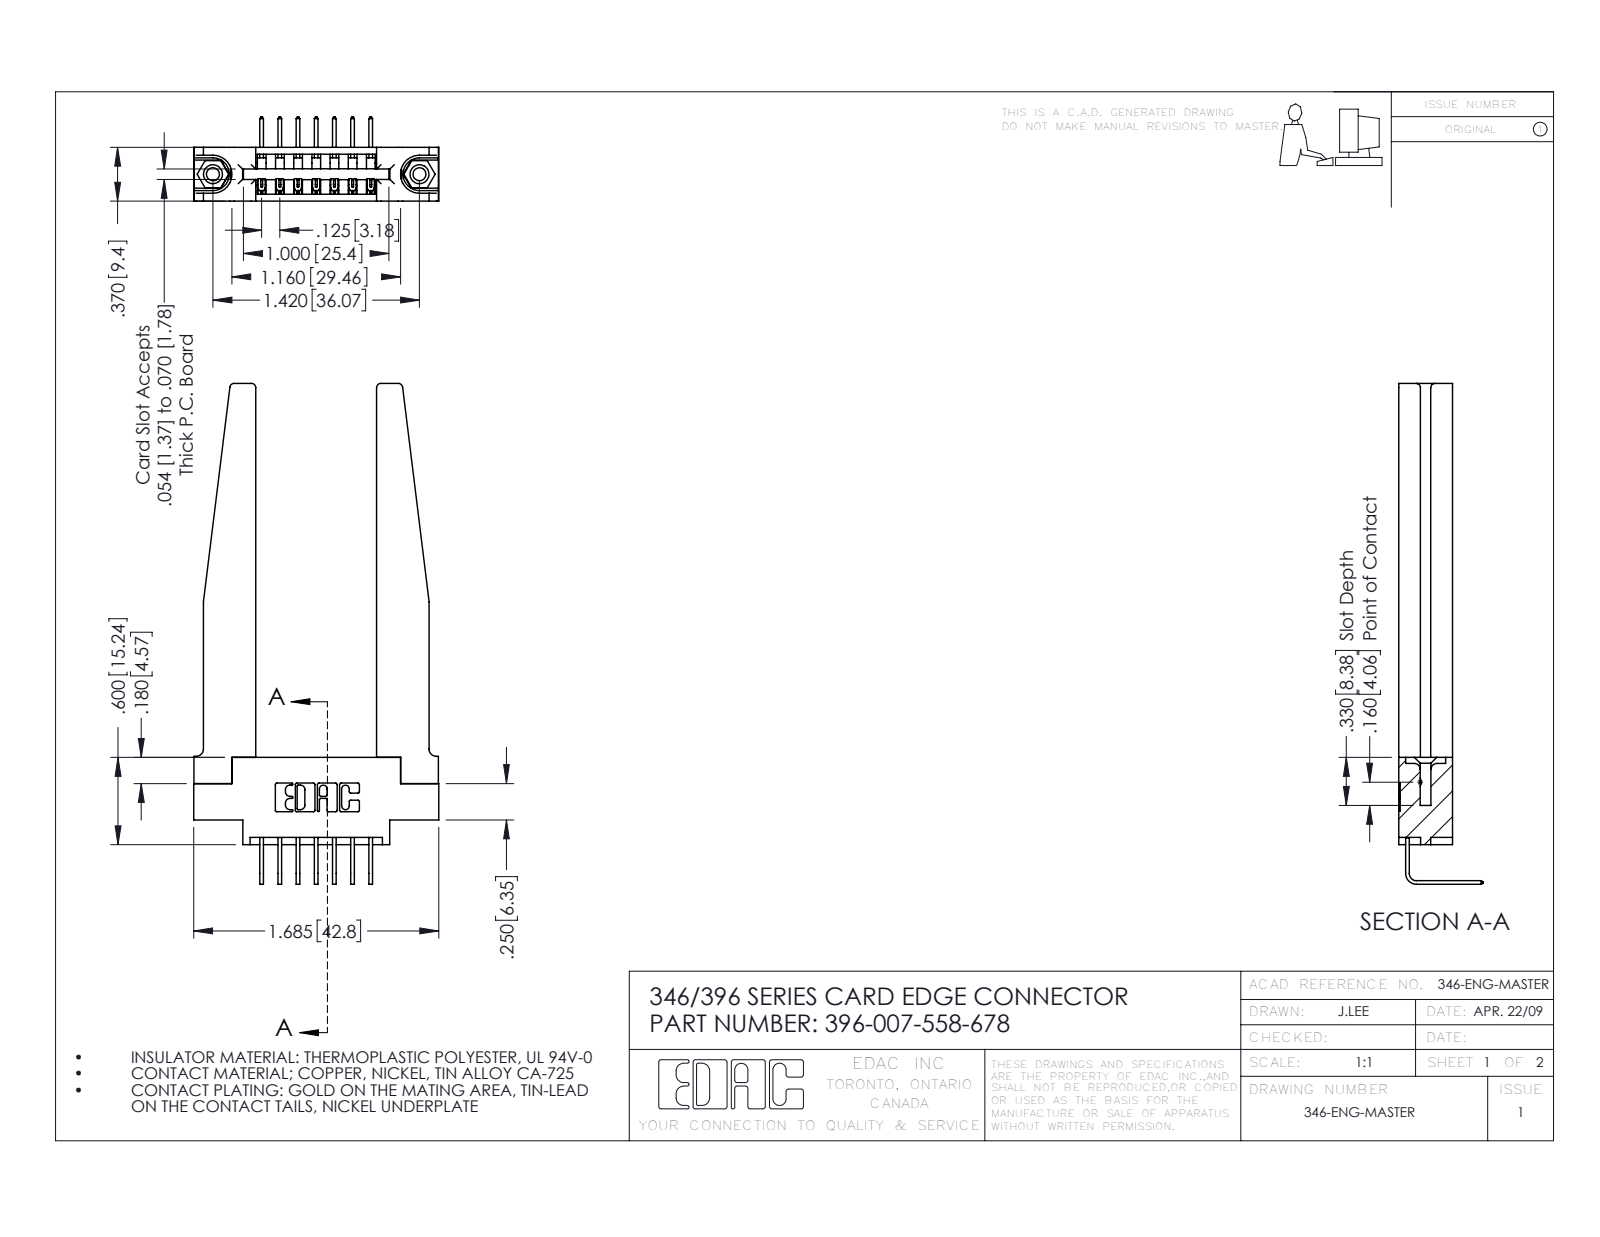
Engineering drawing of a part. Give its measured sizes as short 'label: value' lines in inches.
name: 346-220-078_345-220-078; 345-292-001_558 Tail - 2; 345-250-001_345-250-001-102; 396-007-558-678 (+1 more)
written by: SolidWorks 2016 (CONFIG_CONTROL_DESIGN)
unit: in
bodies: 12 solids, 780 faces (516 planar, 212 cylindrical, 52 other)
size: 3.443 × 1.685 × 0.58
volume: 0.649 in³; area: 17.23 in²
holes: 2× ⌀0.089, 2× ⌀0.125, 2× ⌀0.156, 1× ⌀0.064
bosses: 2× ⌀0.155
rounds: 22× R0.01, 14× R0.006, 8× R0.03, 6× R0.007, 6× R0.031, 3× R0.026, 3× R0.05, 2× R0.031
face distances: 0.37, 0.15, 0.22, 0.831, 0.25, 0.072, 0.148, 0.322, 0.048, 0.102
hole spacings: 0.246, 1.217, 1.42
